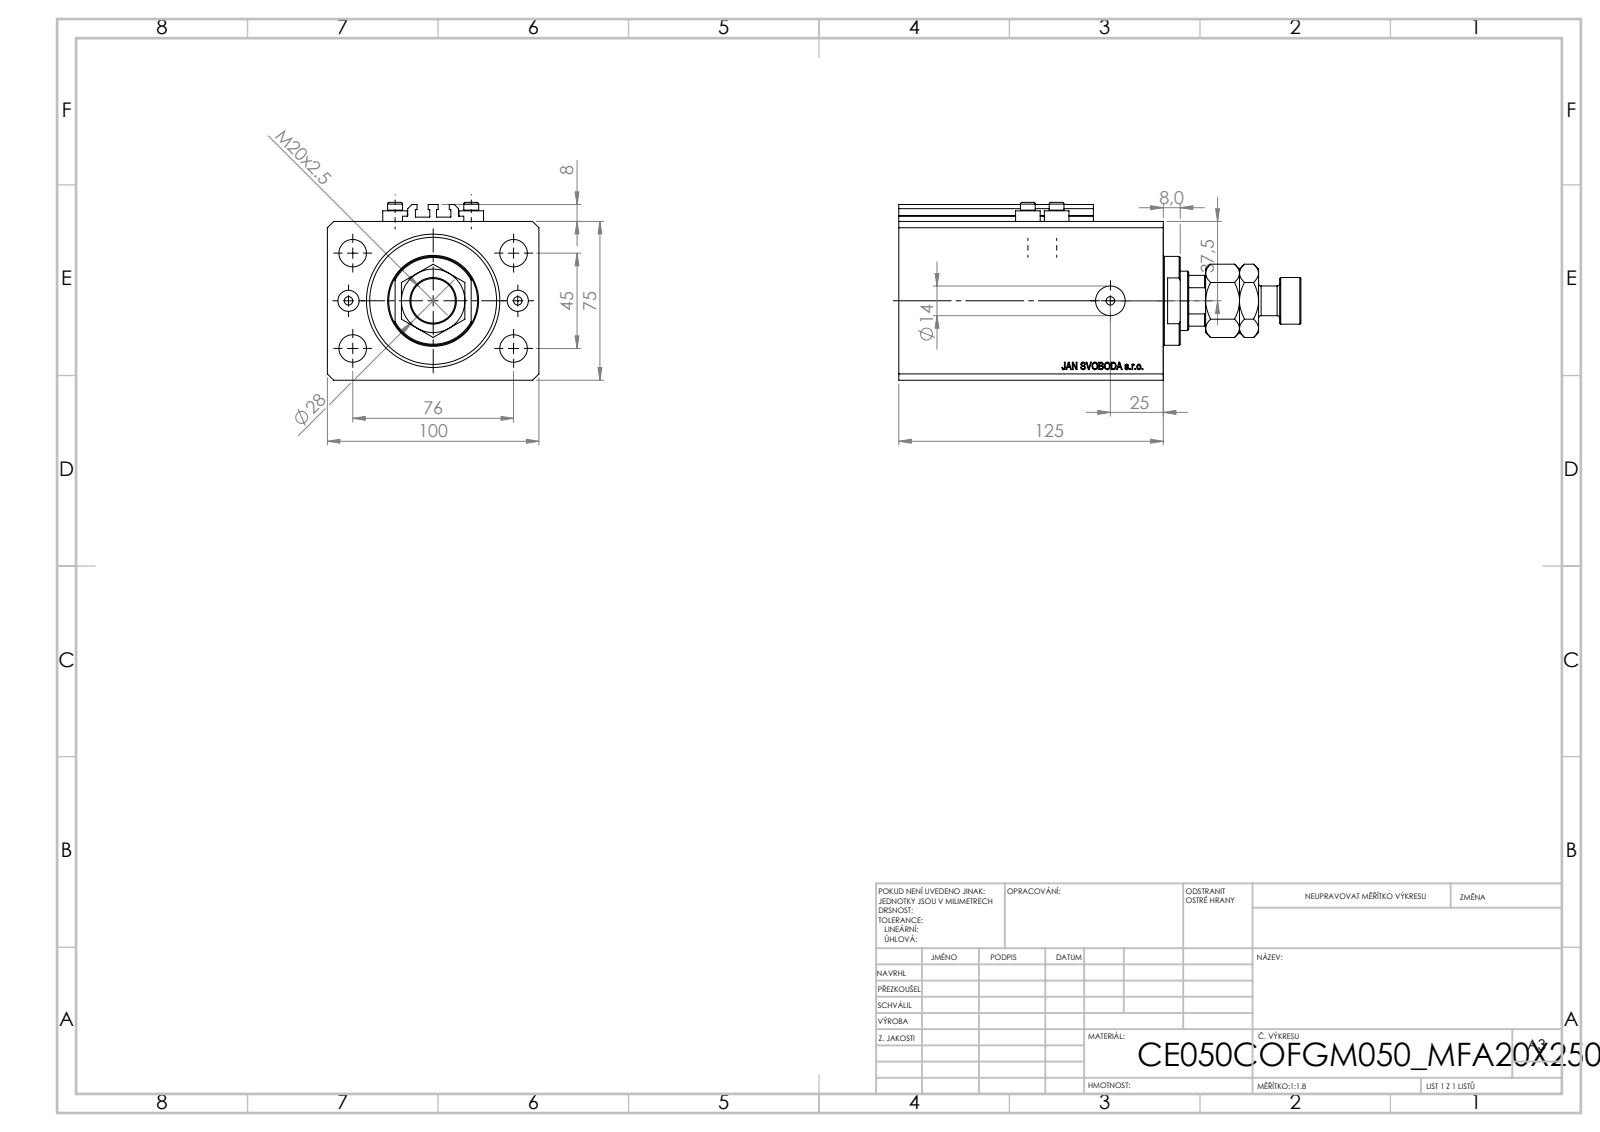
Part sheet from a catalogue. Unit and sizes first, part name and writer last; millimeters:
Units: millimetres
Overall size (bounding box): 189.9 × 100 × 84
Round holes (diameter × count): ⌀4 ×8, ⌀13 ×4, ⌀10 ×2, ⌀14 ×2, ⌀18.5 ×1, ⌀28 ×1, ⌀50 ×1, ⌀63 ×1
Round bosses / shafts (diameter × count): ⌀11.6 ×4, ⌀7 ×4, ⌀42 ×1, ⌀22 ×1, ⌀14 ×1
Partial cylindrical surfaces — rounded edges, fillets, slot ends (radius × count): R0.2 ×10, R13.5 ×1
Main face-to-face distances: 75, 100, 125, 11.9, 113.1, 98.4, 86.5, 26.6, 3, 48.4
Hole centre spacings: 22.59, 44.16, 81.18, 13.6, 36, 38.48, 40, 45
Volume: 844 532 mm³ · Surface area: 149 872 mm²
Bodies: 9 solids, 1086 faces (520 planar, 90 cylindrical, 476 other)
Part name (STEP PRODUCT): MFA; ALLEN BOLT V250CE; V250CE_C_VCP; V250CE_C_Body (+1 more)
STEP written by: SolidWorks 2019 (CONFIG_CONTROL_DESIGN)
